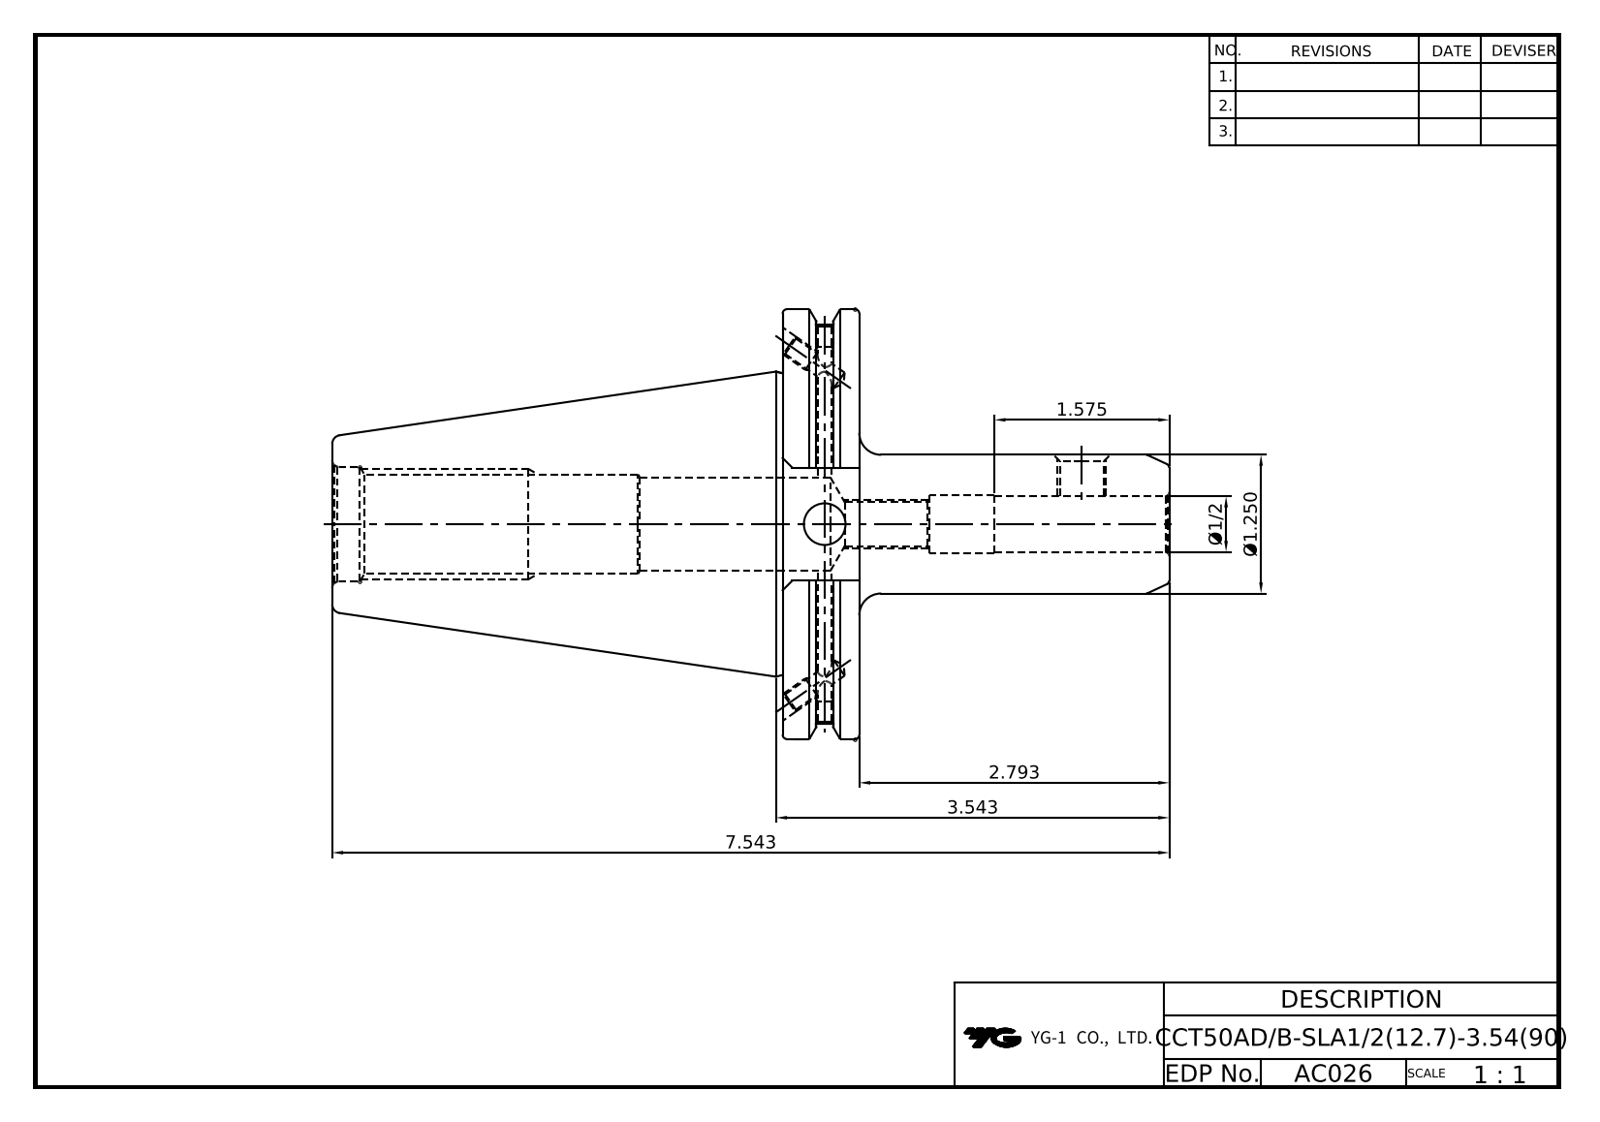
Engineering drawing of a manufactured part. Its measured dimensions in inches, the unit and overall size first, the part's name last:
Units: inches
Overall size (bounding box): 7.543 × 3.875 × 3.728
Round holes (diameter × count): ⌀0.128 ×2, ⌀0.163 ×2, ⌀0.165 ×2, ⌀0.197 ×2, ⌀0.37 ×1, ⌀0.375 ×1, ⌀0.383 ×1, ⌀0.5 ×1, ⌀0.547 ×1, ⌀0.865 ×1, ⌀1.031 ×1
Round bosses / shafts (diameter × count): ⌀3.875 ×1, ⌀3.594 ×1, ⌀2.726 ×1, ⌀1.25 ×1
Main face-to-face distances: 0.691, 4.059, 4.75, 2.875, 7.543, 3.484, 2.793, 1.02, 4.075, 0.016
Volume: 22.66 in³ · Surface area: 85.07 in²
Bodies: 1 solid, 90 faces (39 planar, 27 cylindrical, 24 other)
Part name (STEP PRODUCT): LO-CCT50ADB-SLA12.7-90
STEP written by: Autodesk Inventor 2025 (AUTOMOTIVE_DESIGN)
